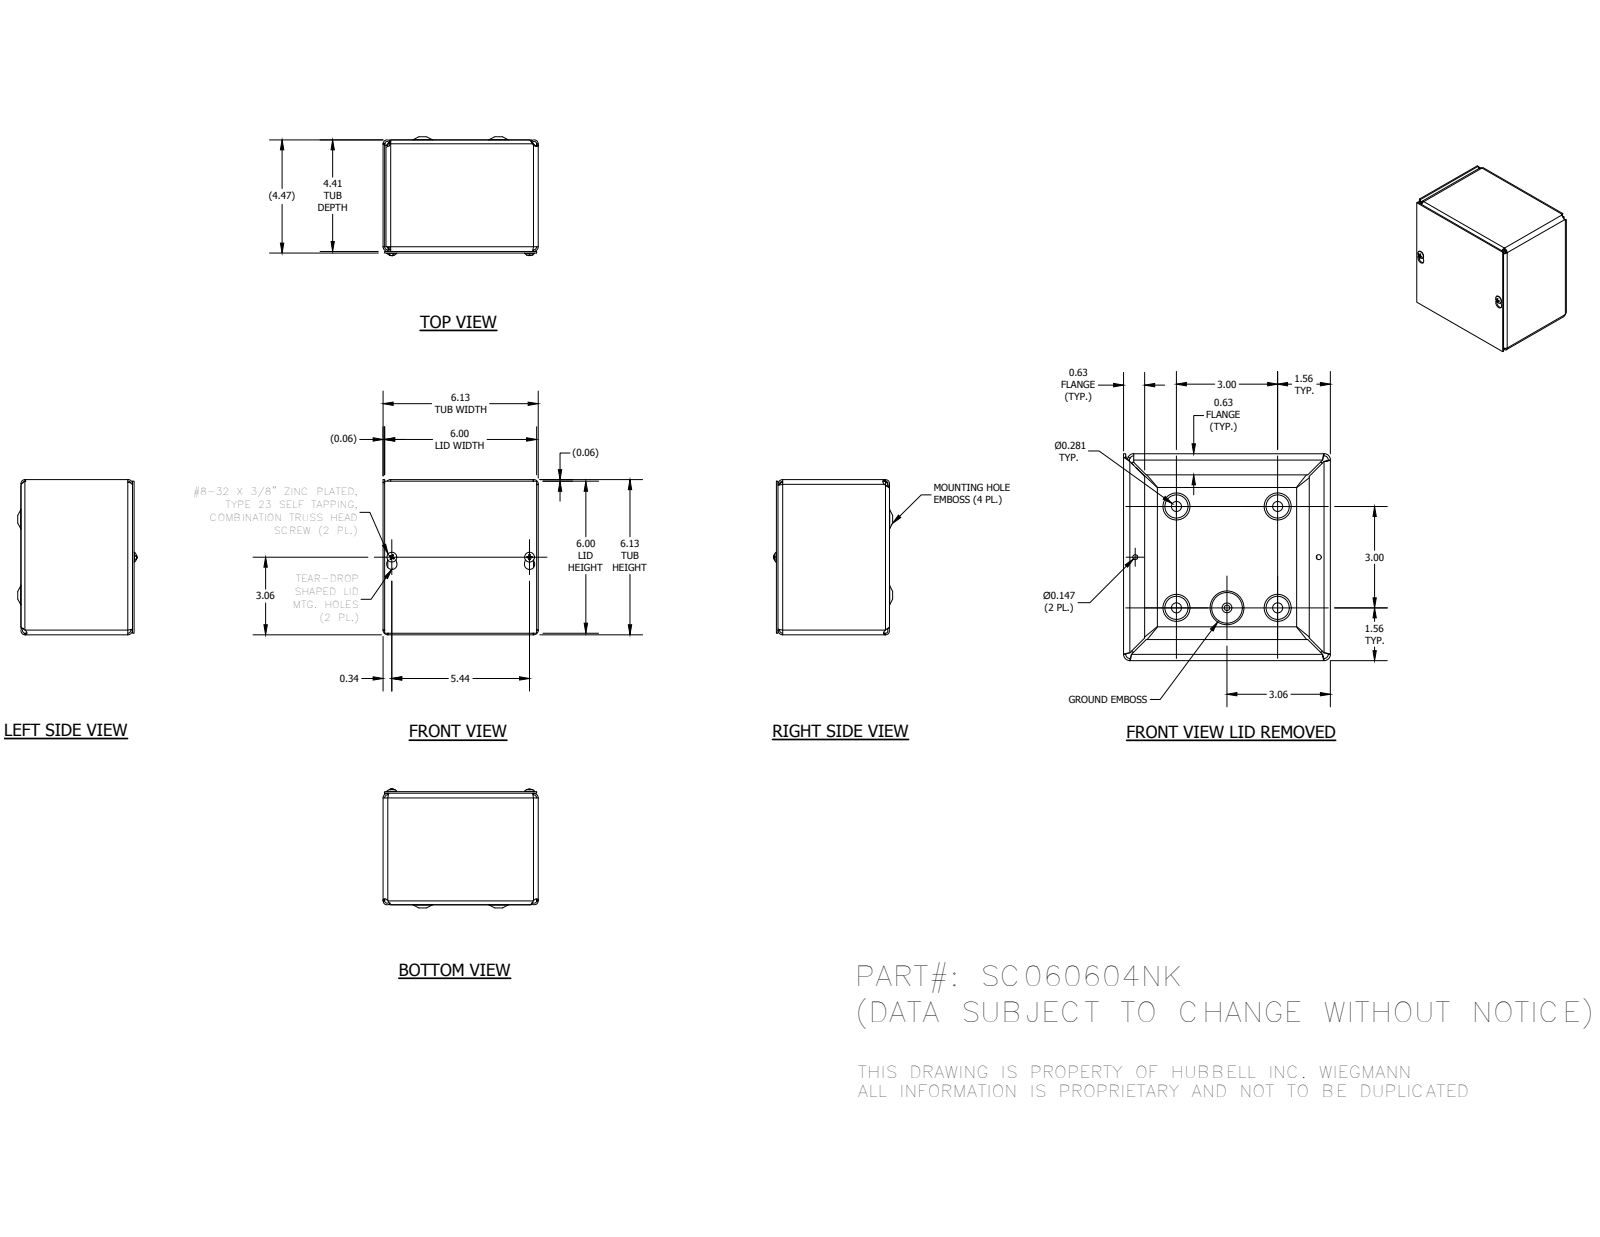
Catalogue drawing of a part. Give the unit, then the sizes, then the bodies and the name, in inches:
Units: inches
Overall size (bounding box): 6.125 × 6.125 × 4.693
Round holes (diameter × count): ⌀0.3 ×4, ⌀0.147 ×2, ⌀0.165 ×1
Round bosses / shafts (diameter × count): ⌀0.384 ×2, ⌀0.164 ×2, ⌀0.228 ×1
Partial cylindrical surfaces — rounded edges, fillets, slot ends (radius × count): R0.125 ×10, R0.187 ×8, R0.055 ×4, R0.062 ×4, R0.094 ×4, R0.117 ×4, R0.124 ×4, R0.156 ×4
Main face-to-face distances: 0.062, 0.062, 4.343, 6.063, 6.125, 6.001, 6.063, 4.405, 0.063, 4.406
Hole centre spacings: 1.933, 3, 1.5, 3.354, 4.243, 4.477, 4.478, 3.105
Volume: 12.61 in³ · Surface area: 414.2 in²
Bodies: 5 solids, 293 faces (108 planar, 57 cylindrical, 128 other)
Part name (STEP PRODUCT): SC0606BKP; SC060604NKWRA; SC0606LID; 34056 (+1 more)
STEP written by: Autodesk Inventor 2014 (AUTOMOTIVE_DESIGN)
